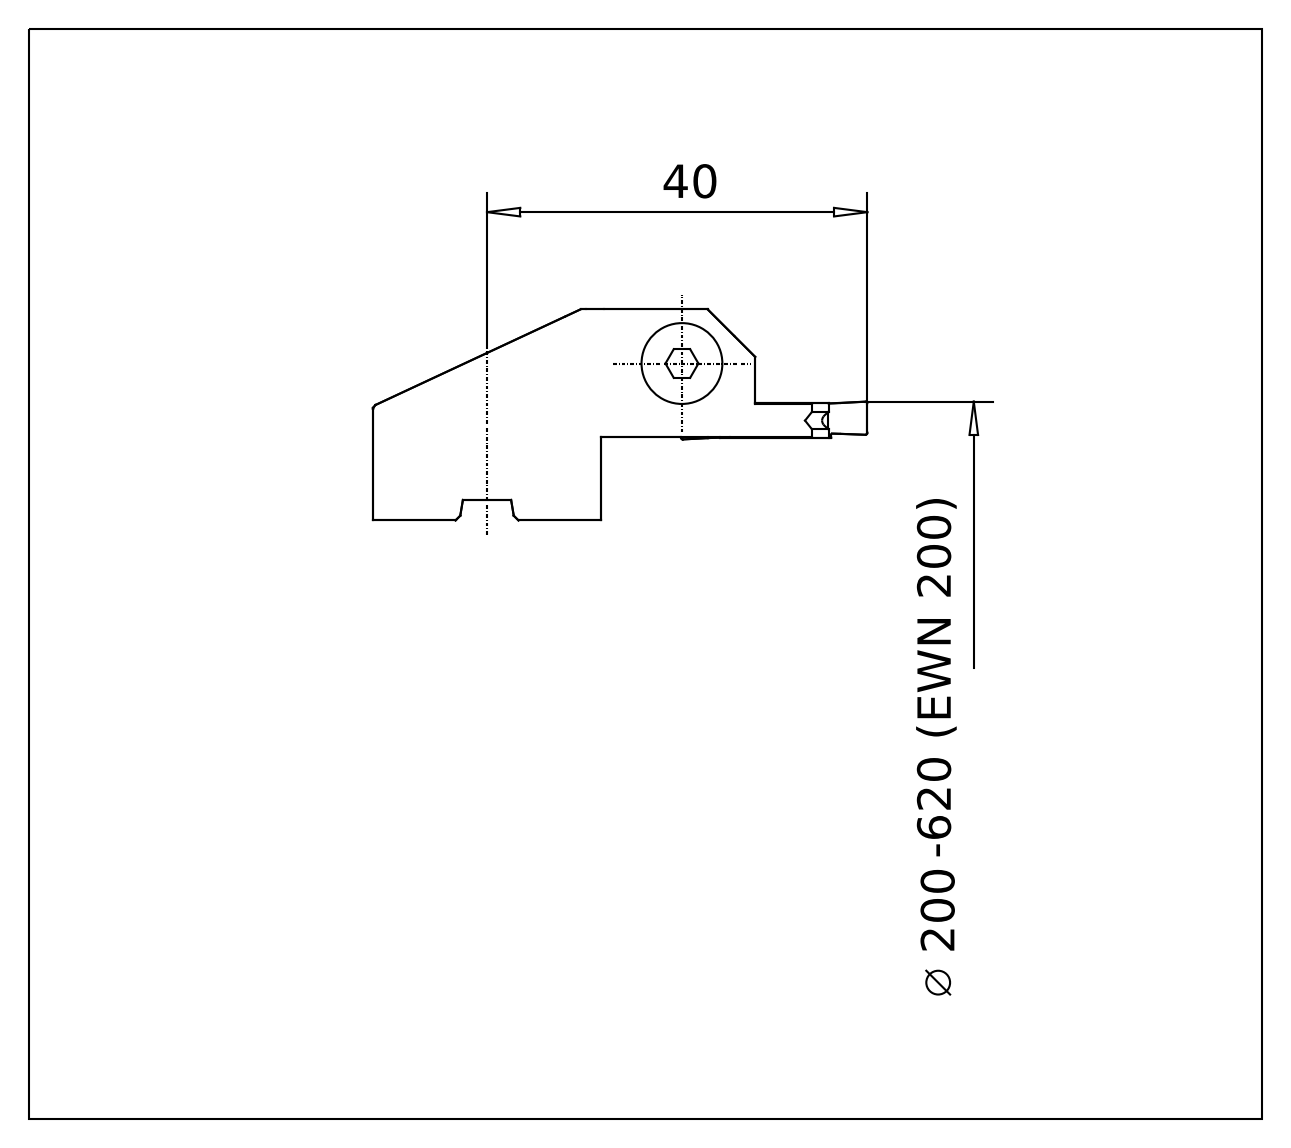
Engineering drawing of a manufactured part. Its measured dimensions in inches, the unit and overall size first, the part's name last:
Units: inches
Overall size (bounding box): 2.047 × 0.945 × 0.874
Round holes (diameter × count): ⌀0.165 ×1, ⌀0.209 ×1, ⌀0.238 ×1, ⌀0.354 ×1, ⌀0.433 ×1
Round bosses / shafts (diameter × count): ⌀0.945 ×1, ⌀0.335 ×1, ⌀0.197 ×1
Partial cylindrical surfaces — rounded edges, fillets, slot ends (radius × count): R0.008 ×4, R0.004 ×2, R0.055 ×2, R0.064 ×2, R0.05 ×1, R0.197 ×1
Main face-to-face distances: 0.344, 0.53, 0.874, 0.492, 0.429, 0.063, 0.161, 0.26, 0.789, 0.085
Hole centre spacings: 0.449
Volume: 0.647 in³ · Surface area: 8.361 in²
Bodies: 3 solids, 143 faces (84 planar, 40 cylindrical, 19 other)
Part name (STEP PRODUCT): 626.938 Kaiser ENH71 S4 200-235|626.938 Kaiser ENH71 S4 200-235;Schnitt-Linear austragen31; 626.938 Kaiser ENH71 S4 200-235|958.435 Kaiser NP4350 P20C_Einstechplatte 4mm;NONE; 626.938 Kaiser ENH71 S4 200-235|690.183 Kaiser ETL M5x12A;Verrundung1
STEP written by: ACIS (automotive_design)
